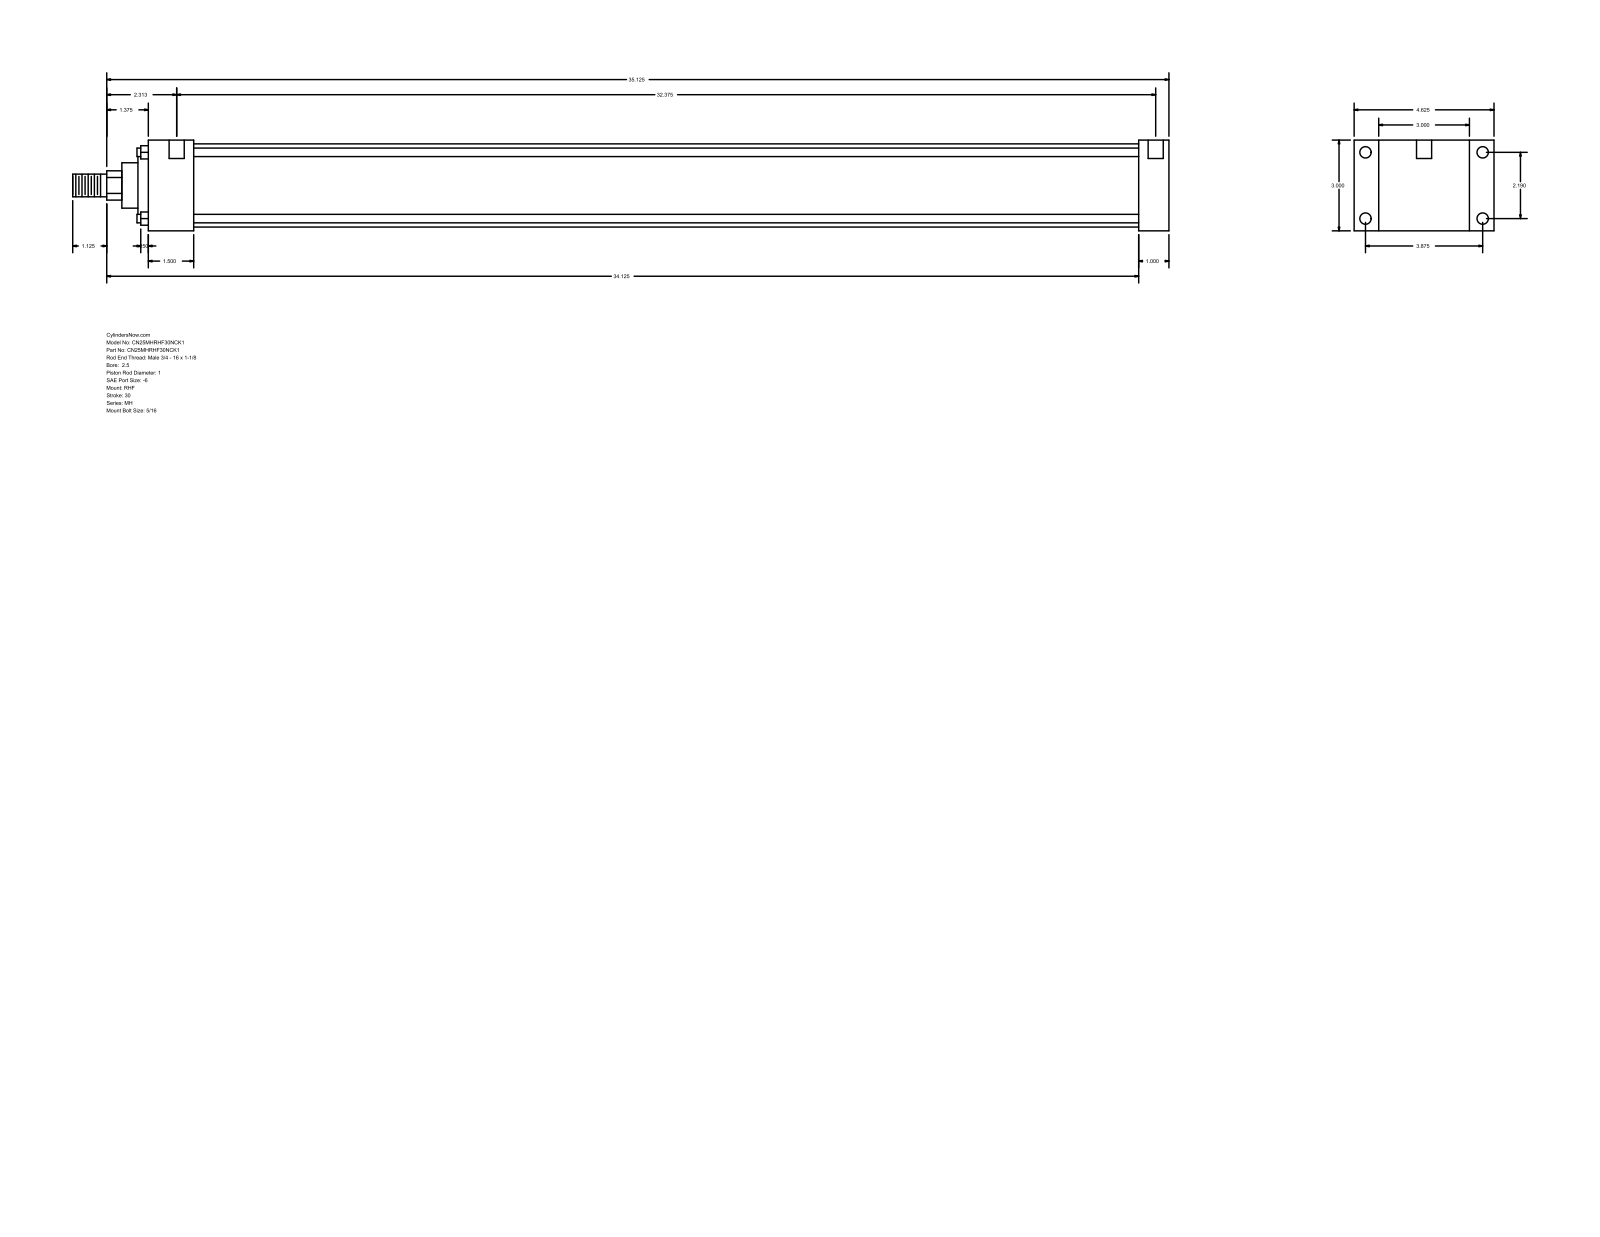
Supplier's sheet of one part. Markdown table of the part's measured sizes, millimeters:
| quantity | value |
| --- | --- |
| part name | MH_RHF__0250_1 |
| STEP written by | GSSL Pune (CONFIG_CONTROL_DESIGN) |
| units | millimeters |
| bodies | 0 solids, 90 faces (61 planar, 29 cylindrical, 0 other) |
| overall size | 920.75 × 117.47 × 76.2 |
| round holes (diameter × count) | 5.56 × 4, 9.53 × 4, 12.7 × 2 |
| round bosses / shafts (diameter × count) | 7.14 × 4, 69.85 × 1, 60.33 × 1, 38.1 × 1, 25.4 × 1, 19.05 × 1 |
| partial cylindrical surfaces (radius × count) | 12.29 × 1 |
| main face-to-face distances | 76.2, 25.4, 20.64, 96.84, 831.85, 857.25, 117.48, 38.11, 793.74, 819.14 |
| hole center spacings | 55.62, 98.42, 113.05, 830.26, 3.18, 4.76, 822.32, 825.5 |
